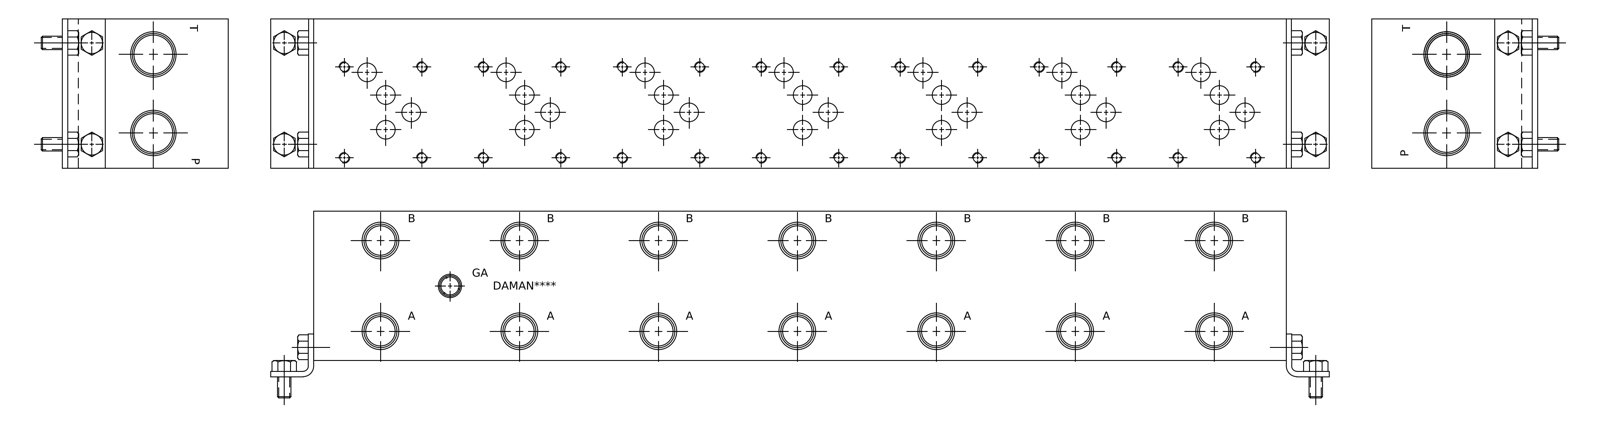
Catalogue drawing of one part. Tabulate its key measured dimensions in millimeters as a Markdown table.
| quantity | value |
| --- | --- |
| part name | Part_AD05P073P_3D |
| STEP written by | Autodesk Inventor 2019 (AUTOMOTIVE_DESIGN) |
| units | millimeters |
| bodies | 1 solid, 934 faces (509 planar, 130 cylindrical, 295 other) |
| overall size | 577.85 × 88.9 × 88.9 |
| volume | 4 403 000 mm³ |
| surface area | 262 009 mm² |
| round holes (diameter × count) | 5.11 × 28, 6.35 × 28, 11.13 × 28, 17.48 × 14, 21.59 × 14, 6.53 × 2, 7.92 × 2, 23.01 × 2, 26.92 × 2, 10.72 × 1, 13.87 × 1 |
| main face-to-face distances | 88.9, 577.85, 15.37, 73.53, 15.85, 562, 1, 69.85, 19.05, 14.37 |
| hole center spacings | 82.55, 165.1, 247.65, 330.2, 98.61, 85.09, 98.17, 173.69 |
